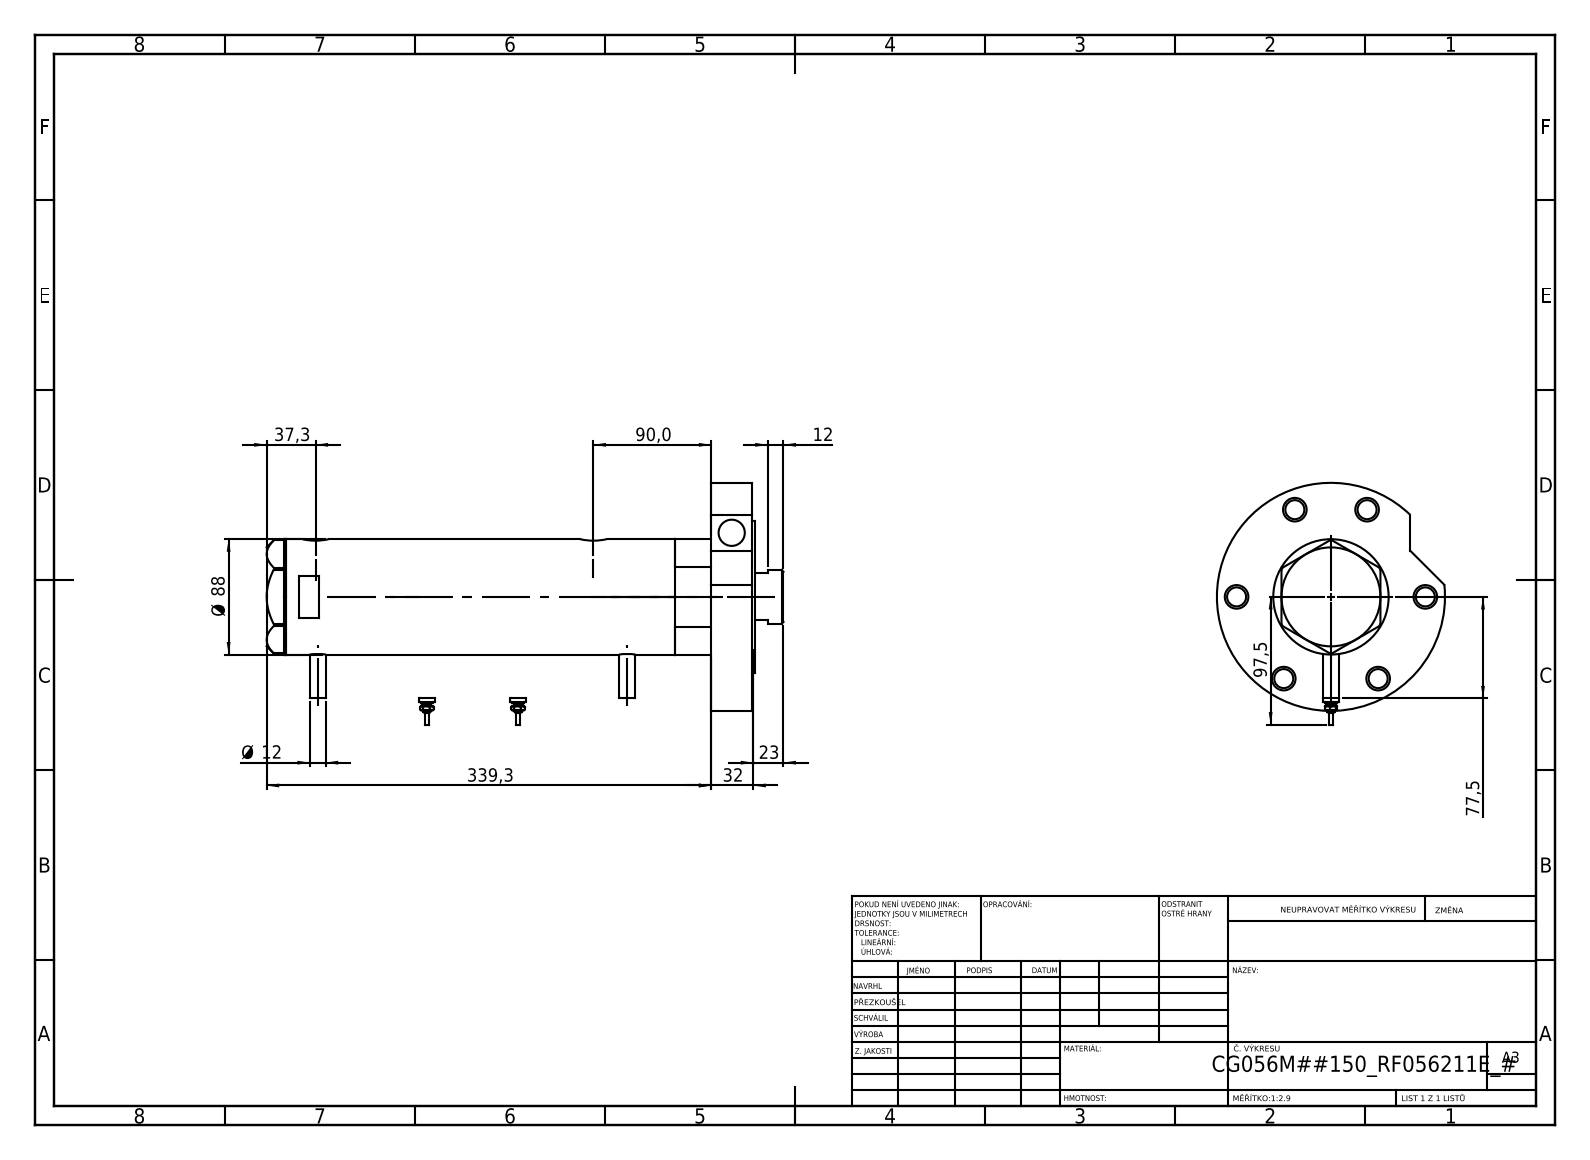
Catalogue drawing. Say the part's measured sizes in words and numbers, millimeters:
The part is named "V270CG_BACK; V270CG_RF211E; V270CG_VC; V270CG_FRONT (+2 more)". Its 3-D file was written by "SolidWorks 2019 (CONFIG_CONTROL_DESIGN)". It is 7 solids with 257 faces: 91 planar, 102 cylindrical and 64 other. Overall it measures 394.3 by 184.5 by 174 millimeters. Its volume is 2 561 000 cubic millimeters and its surface area 360 691 square millimeters. Round holes: 7 of diameter 14.5, 6 of diameter 18, 3 of diameter 20, 2 of diameter 12.5, 2 of diameter 13.16, 1 of diameter 42, 1 of diameter 43.5, 1 of diameter 56, 1 of diameter 60, 1 of diameter 75, 1 of diameter 80. Round bosses or shafts: 4 of diameter 12, 2 of diameter 9, 2 of diameter 7, 2 of diameter 4.5, 2 of diameter 2.5, 1 of diameter 174, 1 of diameter 116, 1 of diameter 88. The main face-to-face distances are 31, 2, 357.3, 324.3, 355.3, 33, 234.4, 89.9, 120.9, 122.9. The hole center spacings are 72, 80, 119.73, 124.71, 129.15, 143.69, 1.7, 25.8.
